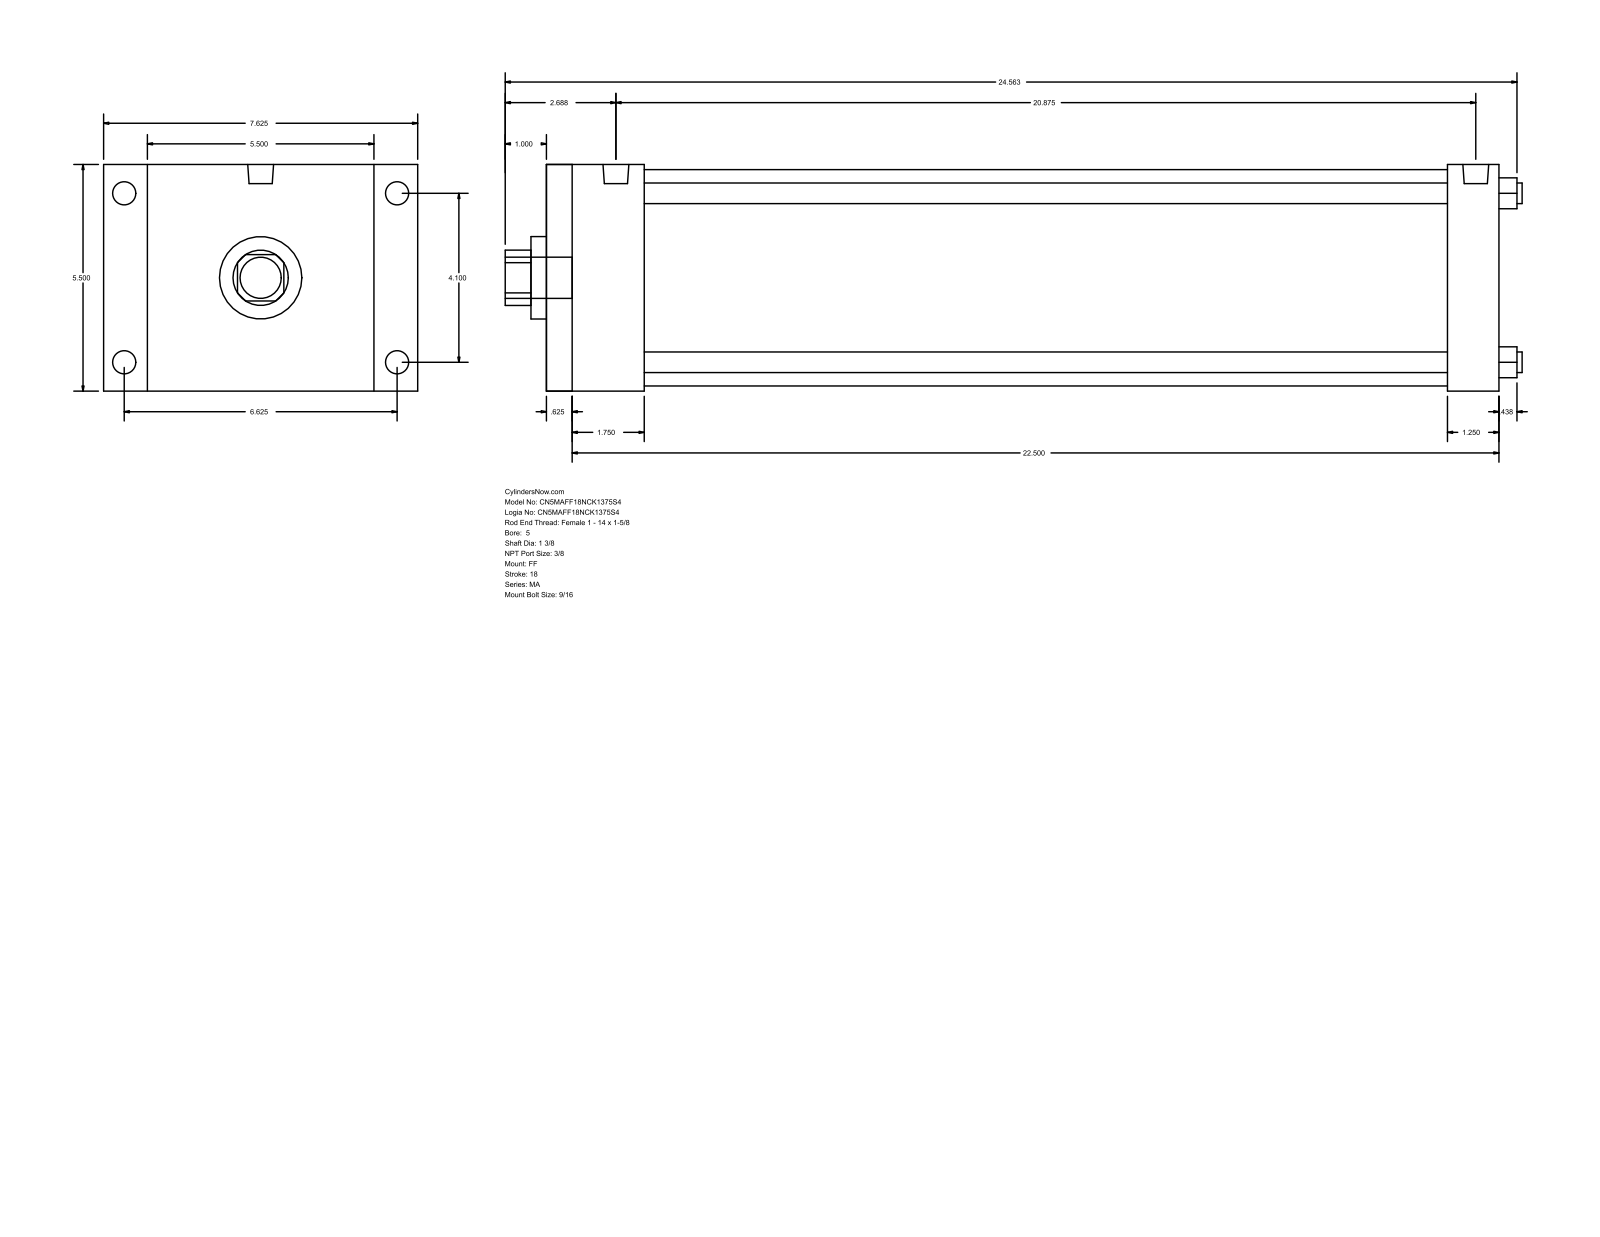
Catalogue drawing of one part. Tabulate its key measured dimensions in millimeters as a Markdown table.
| quantity | value |
| --- | --- |
| part name | MA_FF__0500_1.375 |
| STEP written by | GSSL Pune (CONFIG_CONTROL_DESIGN) |
| units | millimeters |
| bodies | 0 solids, 92 faces (64 planar, 28 cylindrical, 0 other) |
| overall size | 627.06 × 193.68 × 139.7 |
| round holes (diameter × count) | 12.7 × 4, 34.92 × 1, 50.8 × 1, 133.35 × 1 |
| round bosses / shafts (diameter × count) | 14.29 × 4, 11.11 × 4, 15.93 × 2, 25.4 × 1 |
| partial cylindrical surfaces (radius × count) | 17.06 × 1 |
| main face-to-face distances | 139.7, 587.37, 15.87, 571.5, 555.62, 539.75, 31.75, 60.32, 44.45, 495.3 |
| hole center spacings | 73.64, 104.14, 147.28 |
